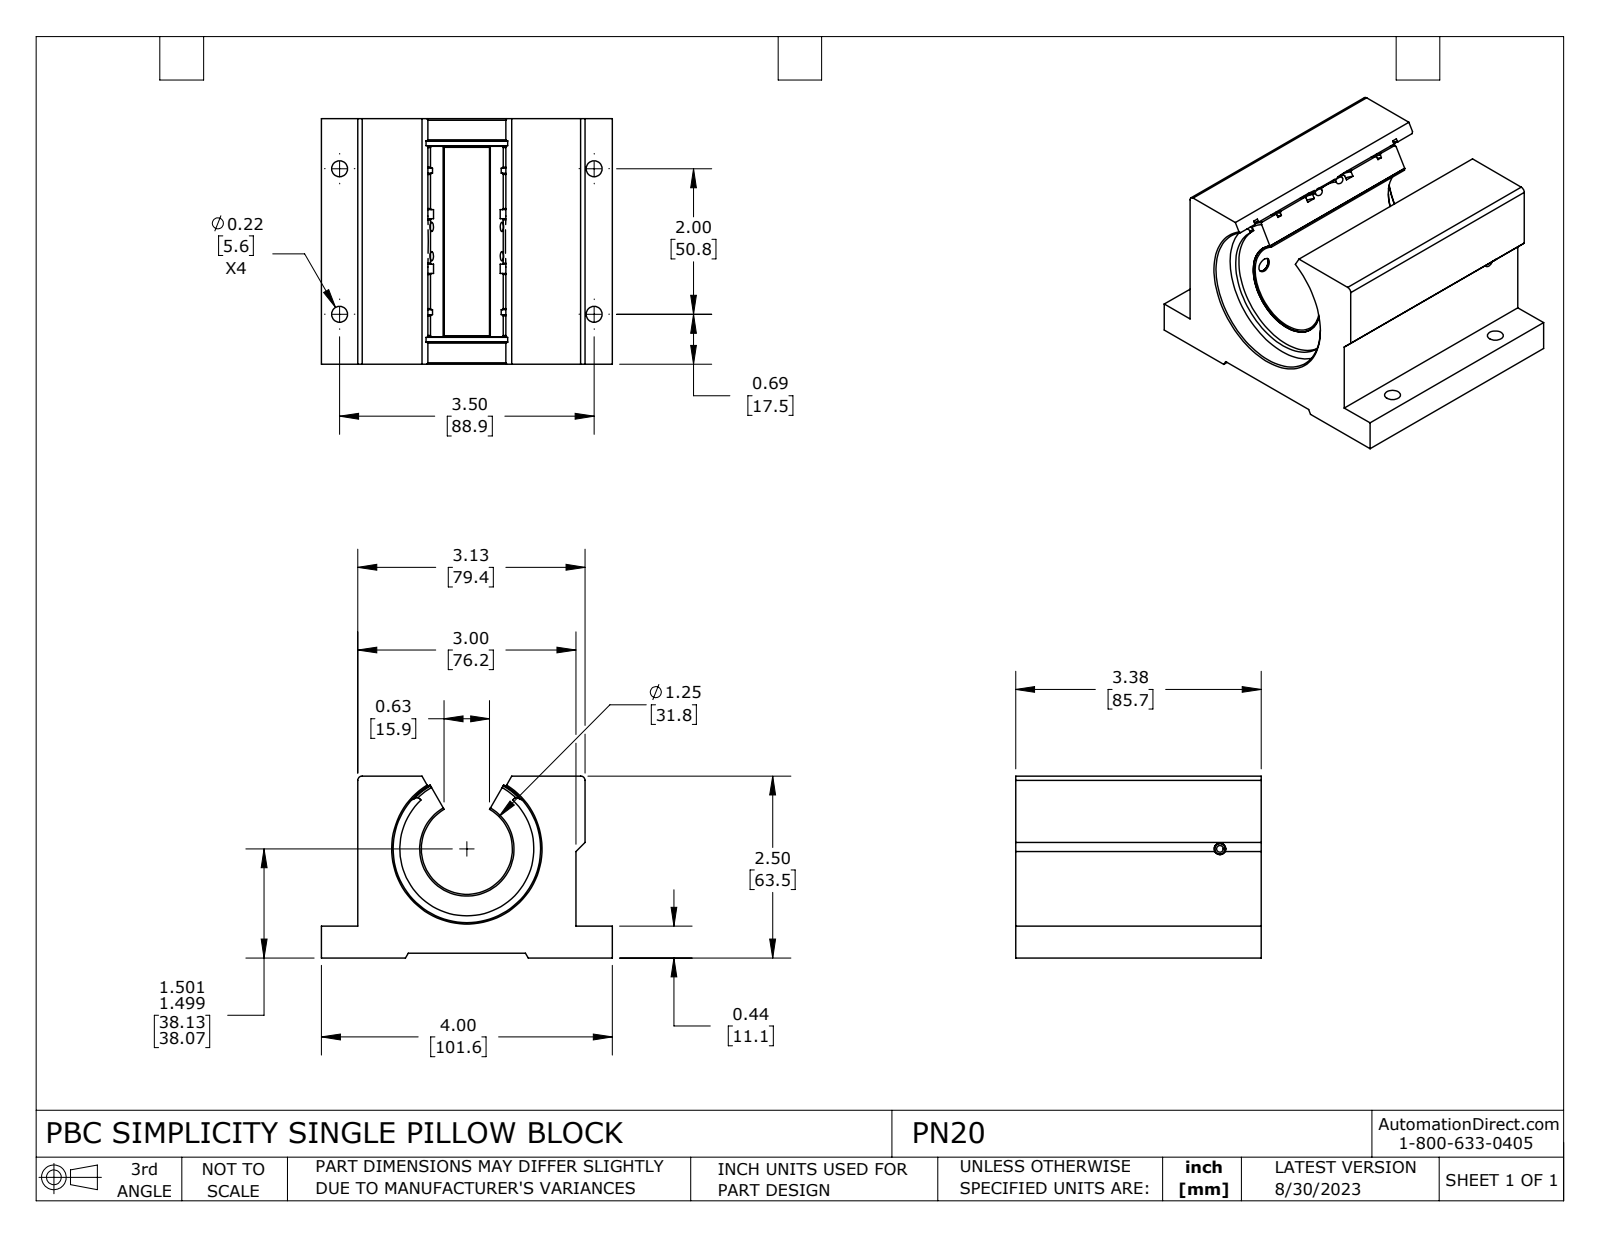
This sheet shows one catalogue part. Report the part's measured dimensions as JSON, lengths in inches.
{"part_name": "PN20", "step_written_by": "SolidWorks 2021 (CONFIG_CONTROL_DESIGN)", "units": "inches", "bodies": {"solids": 8, "faces": 203, "planar": 53, "cylindrical": 94, "other": 56}, "overall_size": [4, 3.375, 2.5], "volume_in3": 19.89, "surface_area_in2": 126, "round_holes": [[0.219, 4], [0.092, 1], [0.157, 1], [0.201, 1], [1.252, 1], [1.295, 1], [2.028, 1], [2.122, 1]], "round_bosses_or_shafts": [[1.999, 1], [1.889, 1], [1.838, 1], [0.156, 1]], "partial_cylinders_radius": [[0.05, 2], [0.06, 2], [0.18, 2], [0.921, 1], [1.077, 1]], "face_to_face_distances": [2.5, 0.065, 2.435, 3.375, 3, 0.437, 0.372, 2.063, 0.379, 0.5], "hole_center_spacings": [2, 3.5, 4.031, 2.243]}
